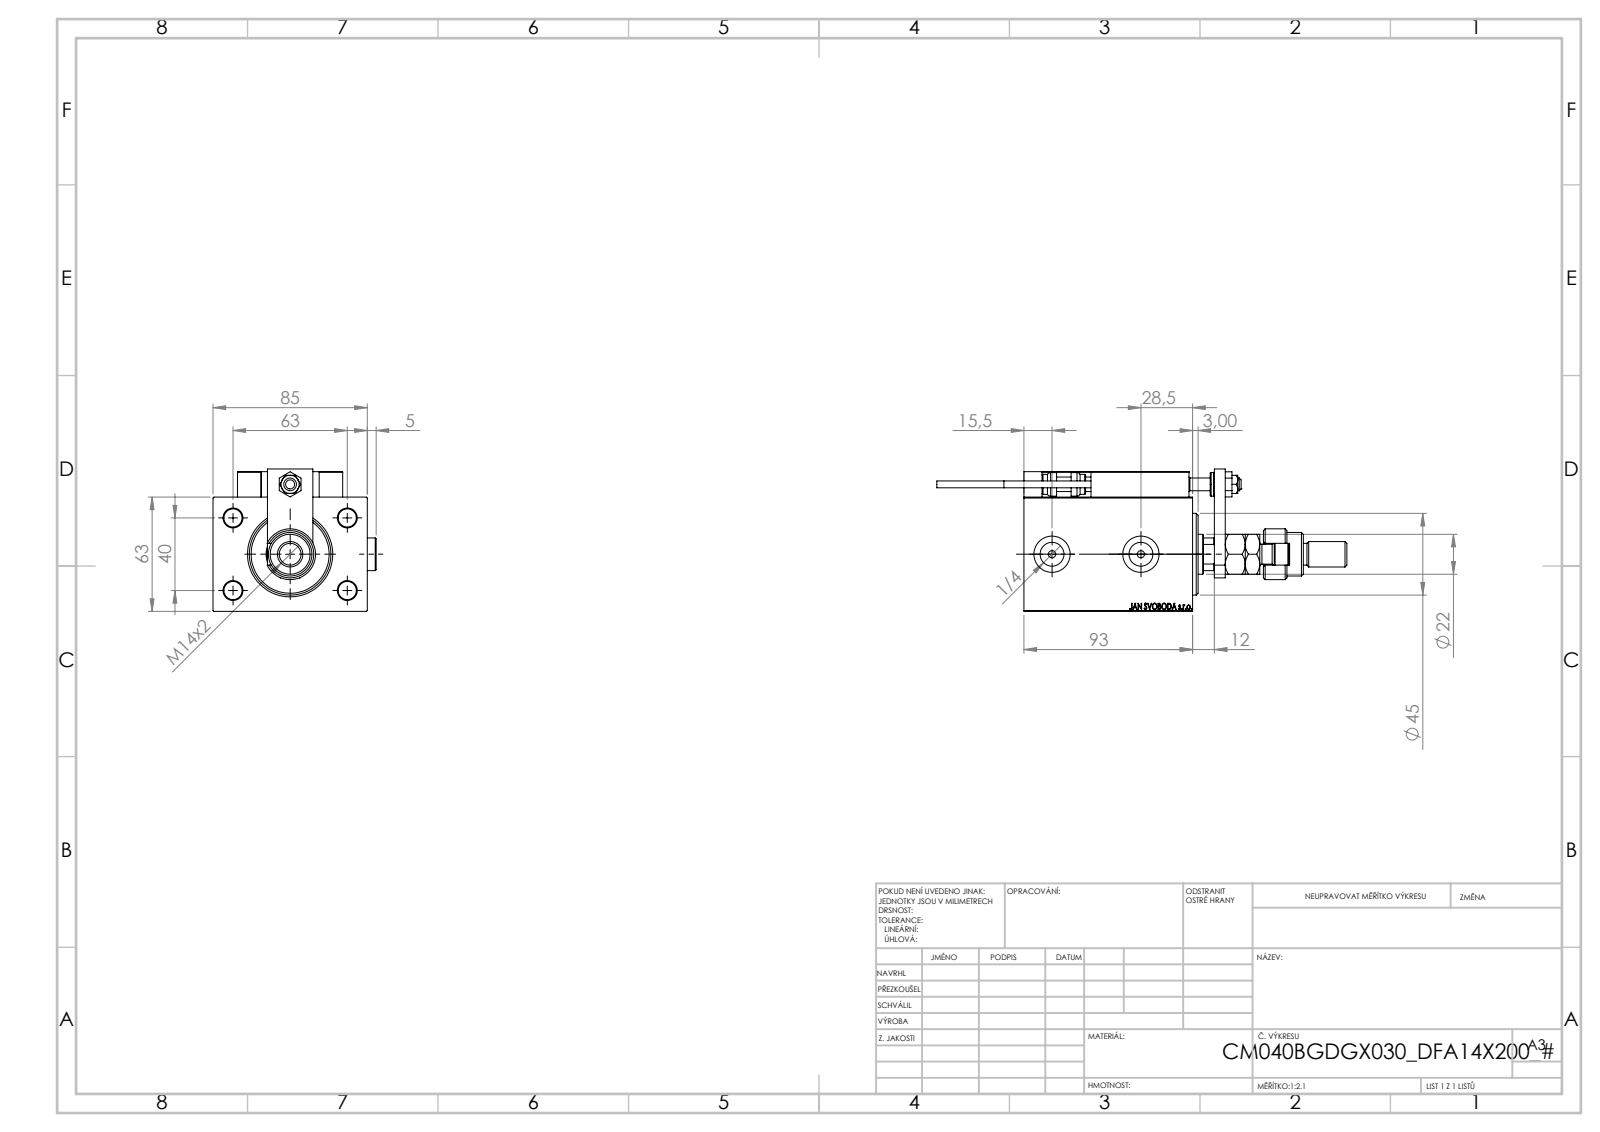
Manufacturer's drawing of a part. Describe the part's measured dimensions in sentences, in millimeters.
The part is named "V450CM_B_Body; SWITCH_X_FRONT_BACK; TYC_L79; MAGNET (+7 more)". Its 3-D file was written by "SolidWorks 2019 (CONFIG_CONTROL_DESIGN)". It is 28 solids with 1457 faces: 623 planar, 213 cylindrical and 621 other. Overall it measures 226 by 89.9 by 78.5 millimeters. Its volume is 528 971 cubic millimeters and its surface area 108 086 square millimeters. Round holes: 6 of diameter 4, 5 of diameter 8, 4 of diameter 3.2, 4 of diameter 10, 2 of diameter 5, 2 of diameter 13.16, 2 of diameter 20, 1 of diameter 7, 1 of diameter 12.5, 1 of diameter 16.5, 1 of diameter 22, 1 of diameter 25.5. Round bosses or shafts: 3 of diameter 18, 2 of diameter 11, 2 of diameter 5, 2 of diameter 3.8, 1 of diameter 28, 1 of diameter 24, 1 of diameter 14, 1 of diameter 13. Partial cylindrical surfaces (rounded edges, fillets, slot ends): 30 of radius 0.3, 2 of radius 3, 1 of radius 9.75, 1 of radius 10.5. The main face-to-face distances are 63, 12, 85, 81, 93, 14, 30, 18, 77, 45. The hole center spacings are 37.31, 11.37, 20, 29.59, 29.69, 36.06, 36.53, 40.
